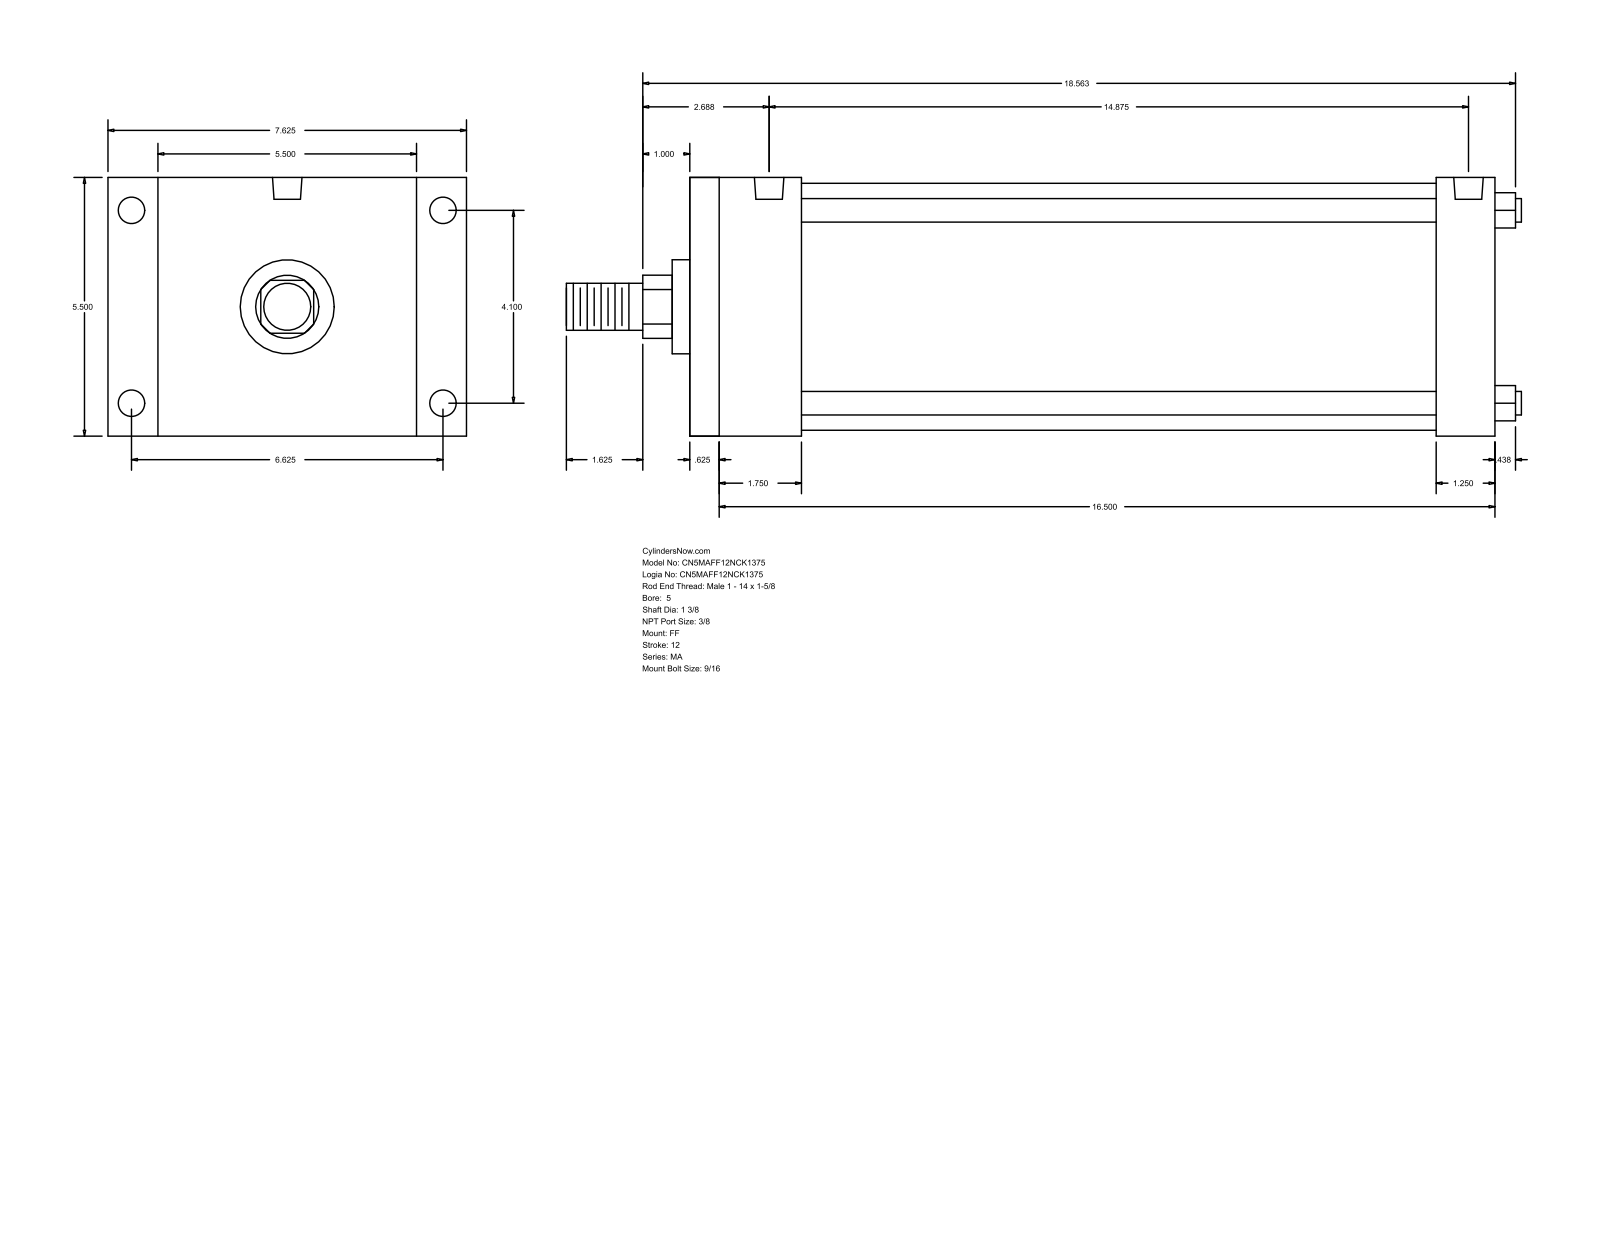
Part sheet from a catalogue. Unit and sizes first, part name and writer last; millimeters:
Units: millimetres
Overall size (bounding box): 515.94 × 193.68 × 139.7
Round holes (diameter × count): ⌀11.11 ×4, ⌀14.29 ×4, ⌀15.93 ×2
Round bosses / shafts (diameter × count): ⌀12.7 ×4, ⌀133.35 ×1, ⌀50.8 ×1, ⌀34.92 ×1, ⌀25.4 ×1
Partial cylindrical surfaces — rounded edges, fillets, slot ends (radius × count): R17.06 ×1
Main face-to-face distances: 139.7, 434.98, 15.87, 419.11, 403.22, 387.35, 31.76, 60.32, 44.45, 342.9
Hole centre spacings: 4.77, 104.14, 168.28, 197.9, 368.29, 373.06, 377.83
Bodies: 0 solids, 92 faces (64 planar, 28 cylindrical, 0 other)
Part name (STEP PRODUCT): MA_FF__0500_1.375
STEP written by: GSSL Pune (CONFIG_CONTROL_DESIGN)
